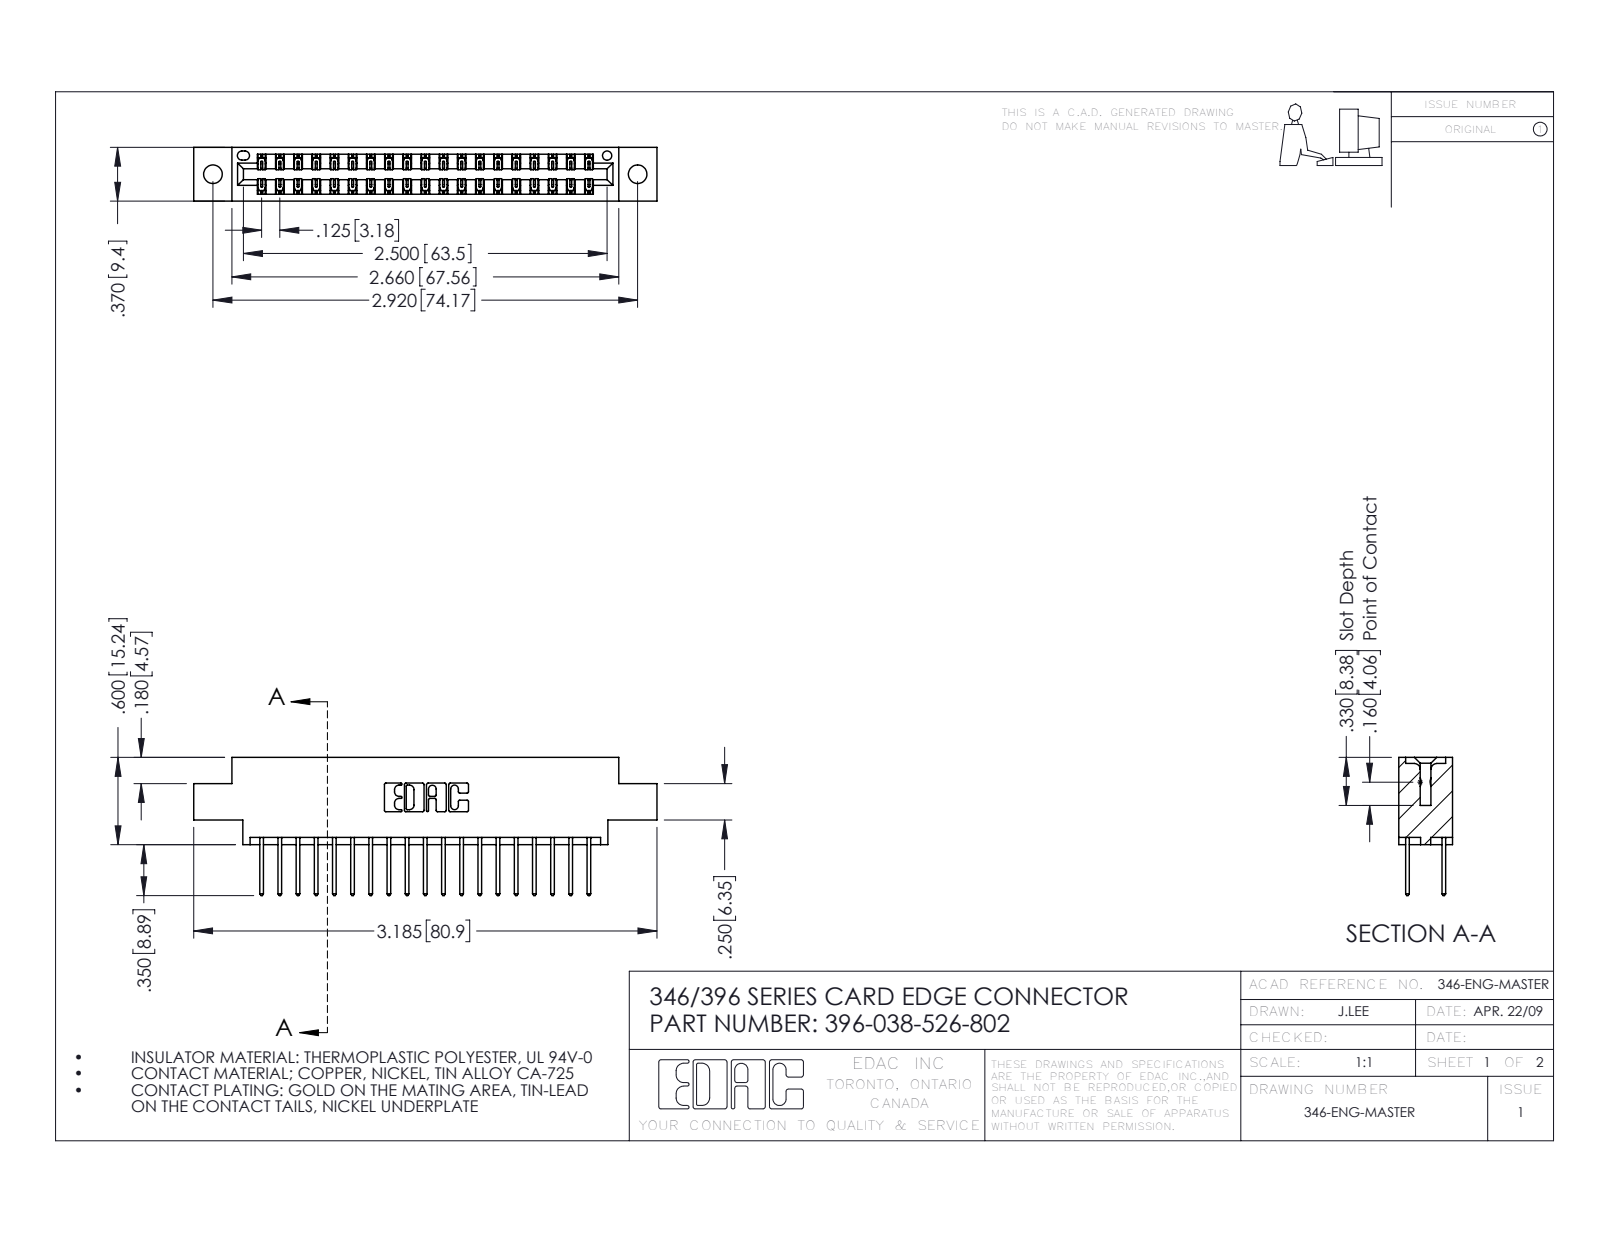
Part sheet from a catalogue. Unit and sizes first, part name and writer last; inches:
Units: inches
Overall size (bounding box): 3.185 × 0.95 × 0.37
Round holes (diameter × count): ⌀0.128 ×2, ⌀0.064 ×1
Partial cylindrical surfaces — rounded edges, fillets, slot ends (radius × count): R0.006 ×57, R0.01 ×38, R0.01 ×22, R0.007 ×6, R0.031 ×6, R0.026 ×3, R0.014 ×2, R0.022 ×2
Main face-to-face distances: 0.048, 0.322, 0.25, 0.37, 0.072, 0.298, 0.025, 0.275, 0.148, 0.222
Hole centre spacings: 0.246, 2.713, 2.92
Volume: 0.463 in³ · Surface area: 15.89 in²
Bodies: 39 solids, 2102 faces (1410 planar, 692 cylindrical, 0 other)
Part name (STEP PRODUCT): 345-292-001_345-293-126; 396-038-526-802; 346 Part_0.170 Offset - 0.128 Dia
STEP written by: SolidWorks 2016 (CONFIG_CONTROL_DESIGN)
